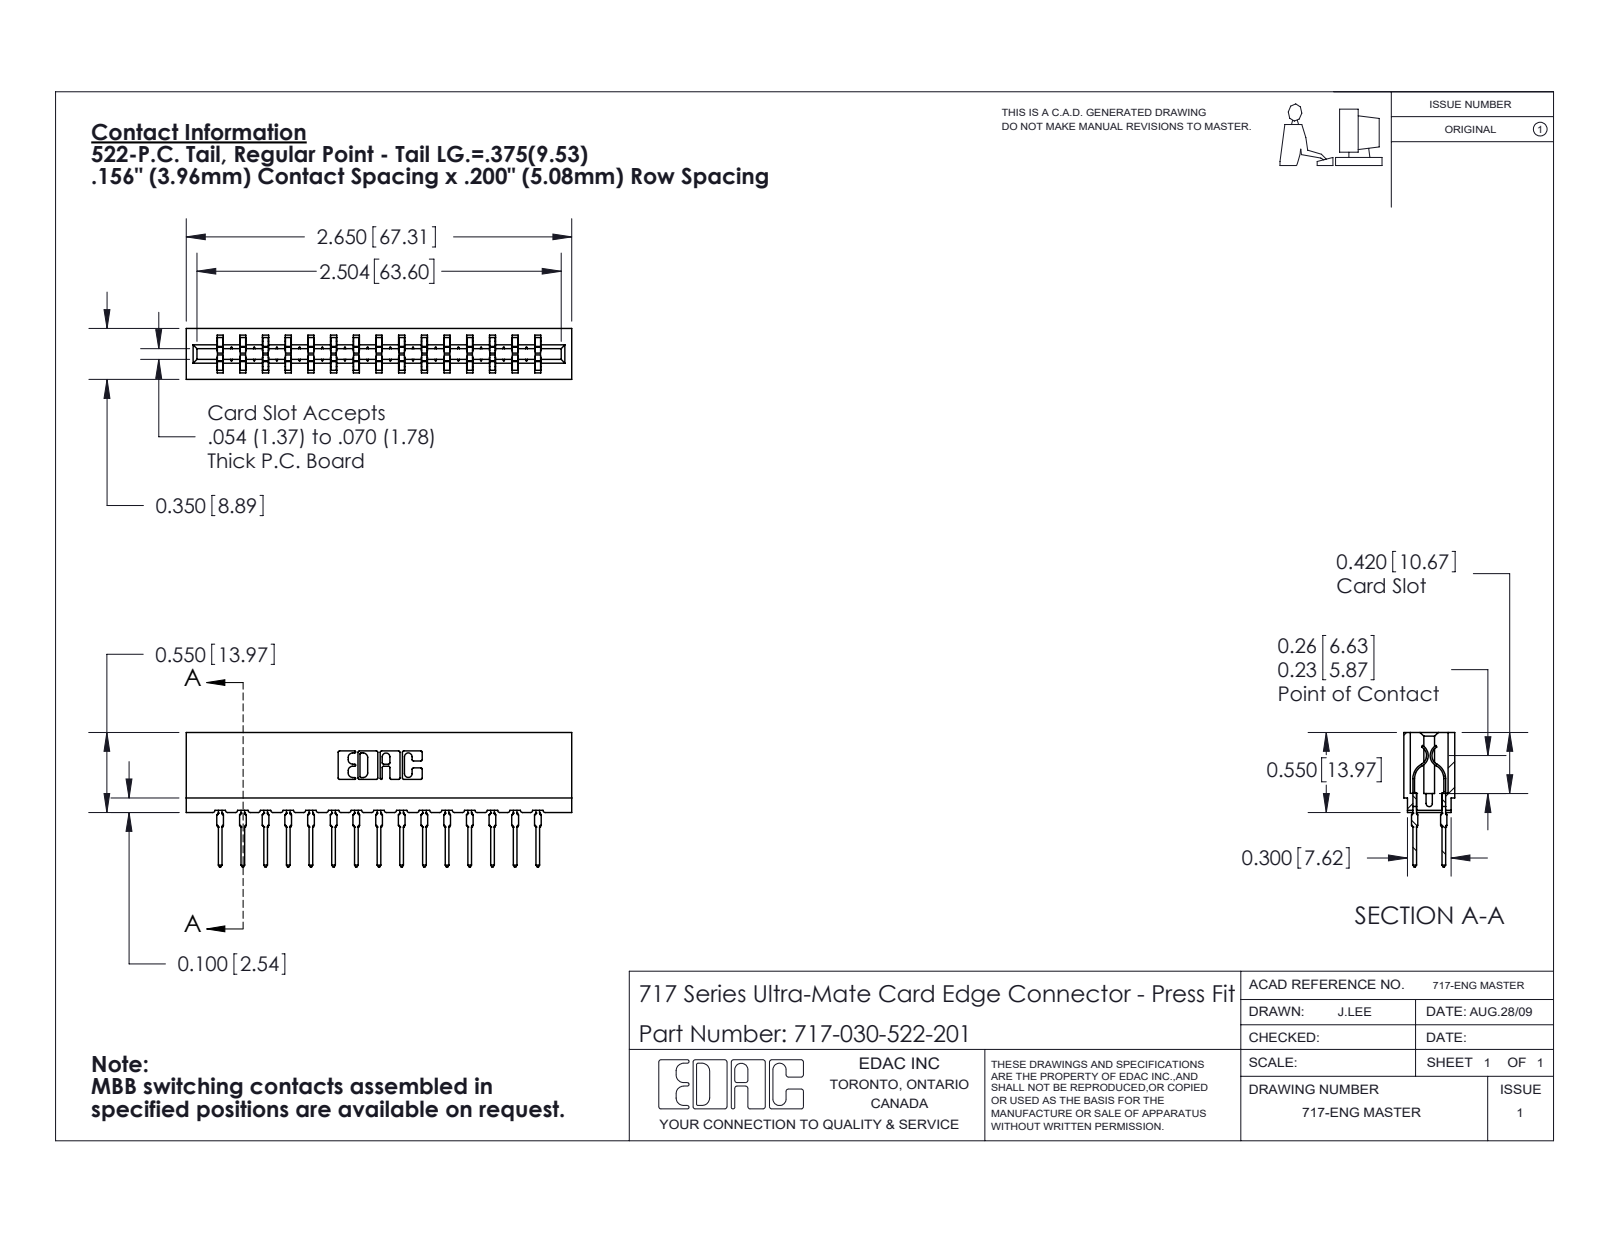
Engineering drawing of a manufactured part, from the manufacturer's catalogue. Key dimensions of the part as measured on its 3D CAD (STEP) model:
Part name (STEP PRODUCT): 745-292-001_522; 717 Part_Insulator Option - 06; 717-030-522-201
STEP written by: SolidWorks 2020 (CONFIG_CONTROL_DESIGN)
Units: inches
Bodies: 31 solids, 2794 faces (1449 planar, 565 cylindrical, 780 other)
Overall size (bounding box): 2.65 × 0.924 × 0.35
Volume: 0.365 in³ · Surface area: 13.79 in²
Partial cylindrical surfaces — rounded edges, fillets, slot ends (radius × count): R0.021 ×60, R0.015 ×30, R0.01 ×22, R0.005 ×8, R0.011 ×8, R0.007 ×6, R0.031 ×6, R0.026 ×3
Main face-to-face distances: 0.212, 0.138, 0.35, 0.156, 0.624, 0.468, 0.063, 0.287, 0.076, 0.149
